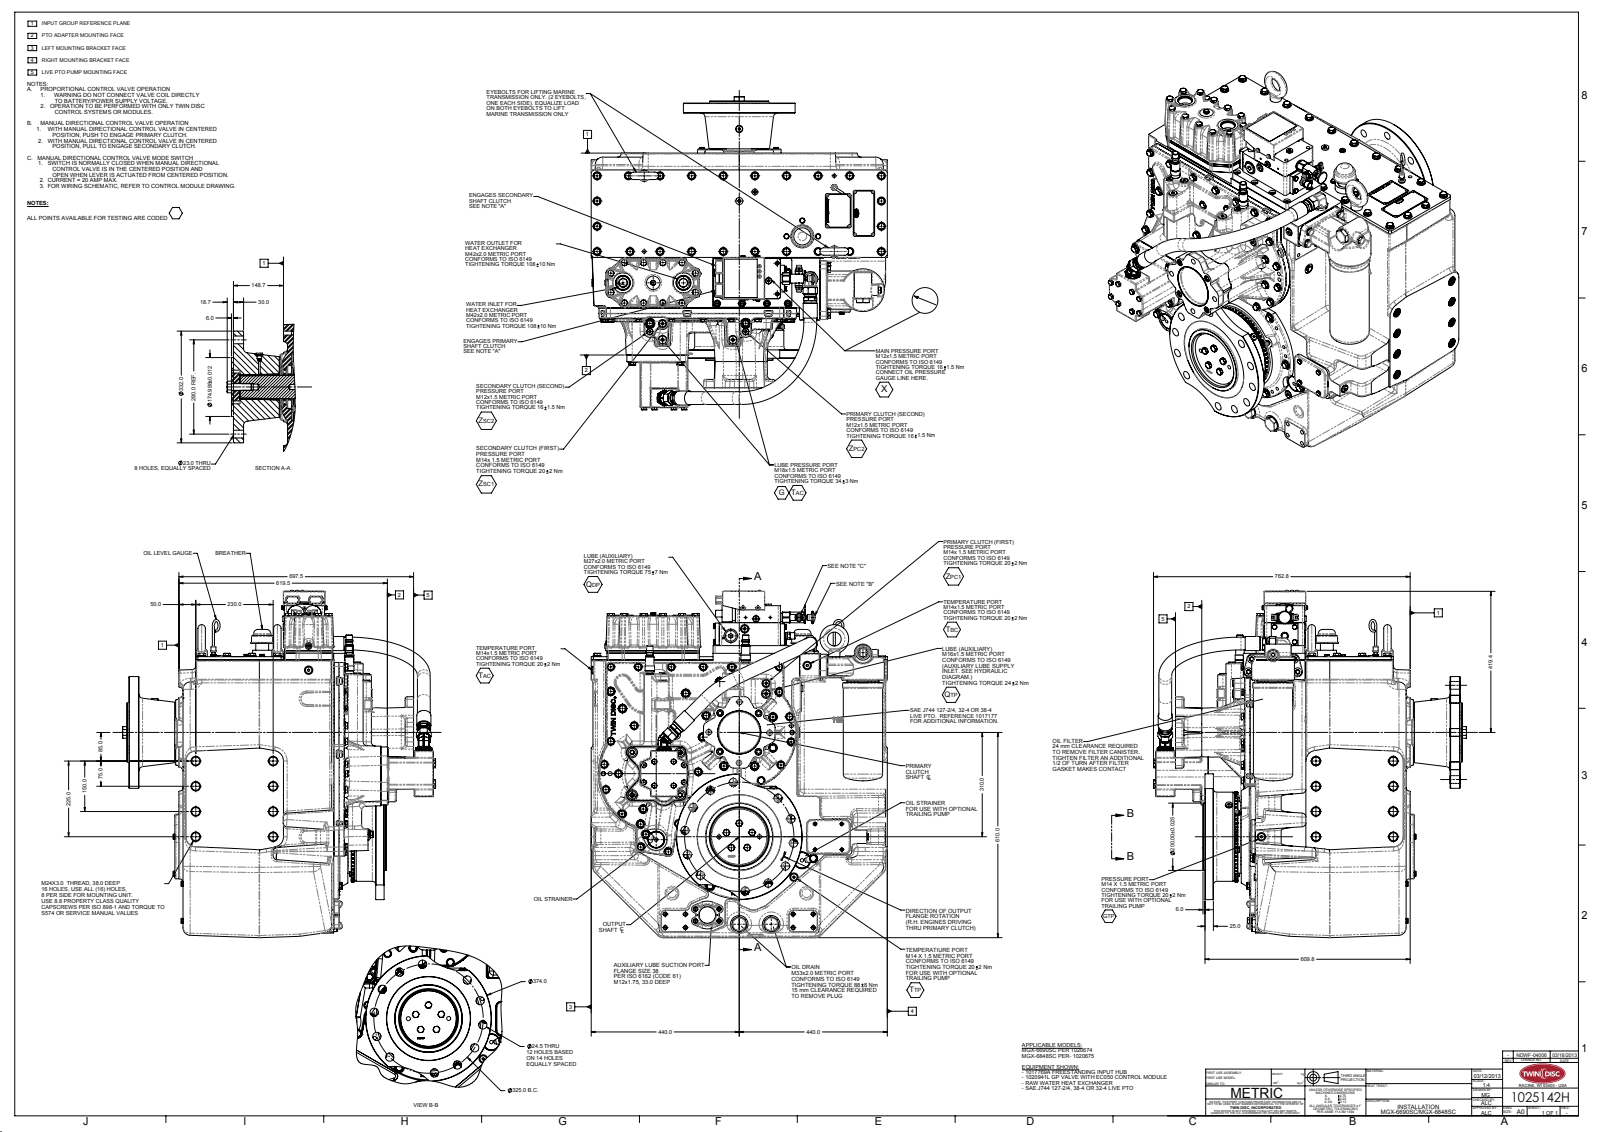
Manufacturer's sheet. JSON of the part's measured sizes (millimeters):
{"part_name": "1025142H", "step_written_by": "SolidWorks 2010 (AUTOMOTIVE_DESIGN)", "units": "millimeters", "bodies": {"solids": 0, "faces": 5516, "planar": 1871, "cylindrical": 1748, "other": 1897}, "overall_size": [1032.84, 930.28, 887.13], "round_holes": [[12, 37], [24.5, 12], [20, 11], [10, 10], [25, 10], [23, 8], [28.24, 8], [26, 7], [10.2, 6], [10.32, 4], [16, 4], [30, 3]], "round_bosses_or_shafts": [[24, 68], [18, 38], [19, 10], [15.32, 7], [38.1, 4], [17, 4], [13, 4], [2.54, 4]], "partial_cylinders_radius": [[3, 150], [6, 116], [43.44, 89], [12, 88], [2.54, 46], [11, 34], [3.05, 33], [22, 30]], "face_to_face_distances": [9.3, 465, 17, 448, 0.79, 16.5, 0.5, 464.5, 12, 10.09], "hole_center_spacings": [371.08, 70, 402.49, 90, 180, 360, 138.92, 75]}
